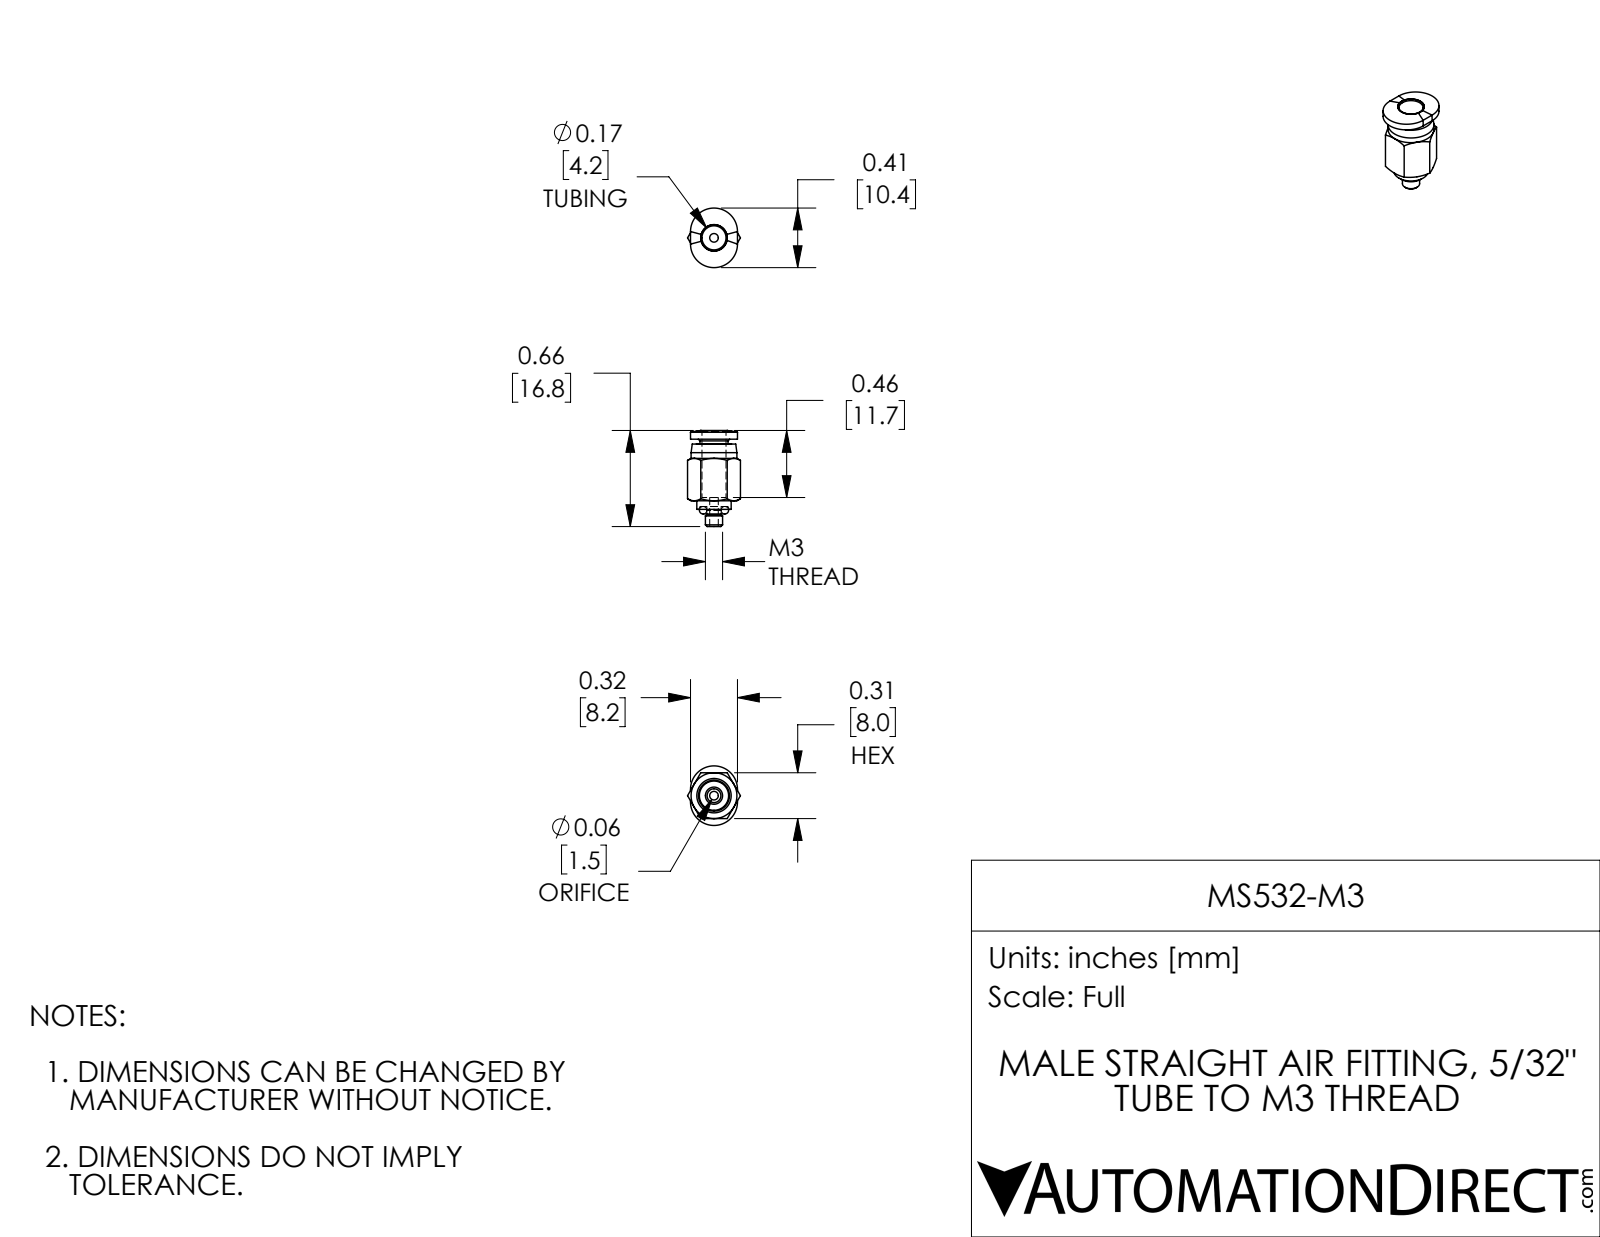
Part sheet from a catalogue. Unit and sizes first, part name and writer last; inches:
Units: inches
Overall size (bounding box): 0.66 × 0.409 × 0.364
Round holes (diameter × count): ⌀0.059 ×1, ⌀0.165 ×1
Round bosses / shafts (diameter × count): ⌀0.315 ×1, ⌀0.24 ×1, ⌀0.236 ×1, ⌀0.193 ×1, ⌀0.118 ×1, ⌀0.098 ×1
Partial cylindrical surfaces — rounded edges, fillets, slot ends (radius × count): R0.161 ×2
Main face-to-face distances: 0.315, 0.423, 0.39, 0.033, 0.039, 0.429, 0.463, 0.062, 0.022, 0.367
Volume: 0.033 in³ · Surface area: 1.251 in²
Bodies: 2 solids, 73 faces (18 planar, 21 cylindrical, 34 other)
Part name (STEP PRODUCT): MS532-M3
STEP written by: SolidWorks 2017 (AUTOMOTIVE_DESIGN)
